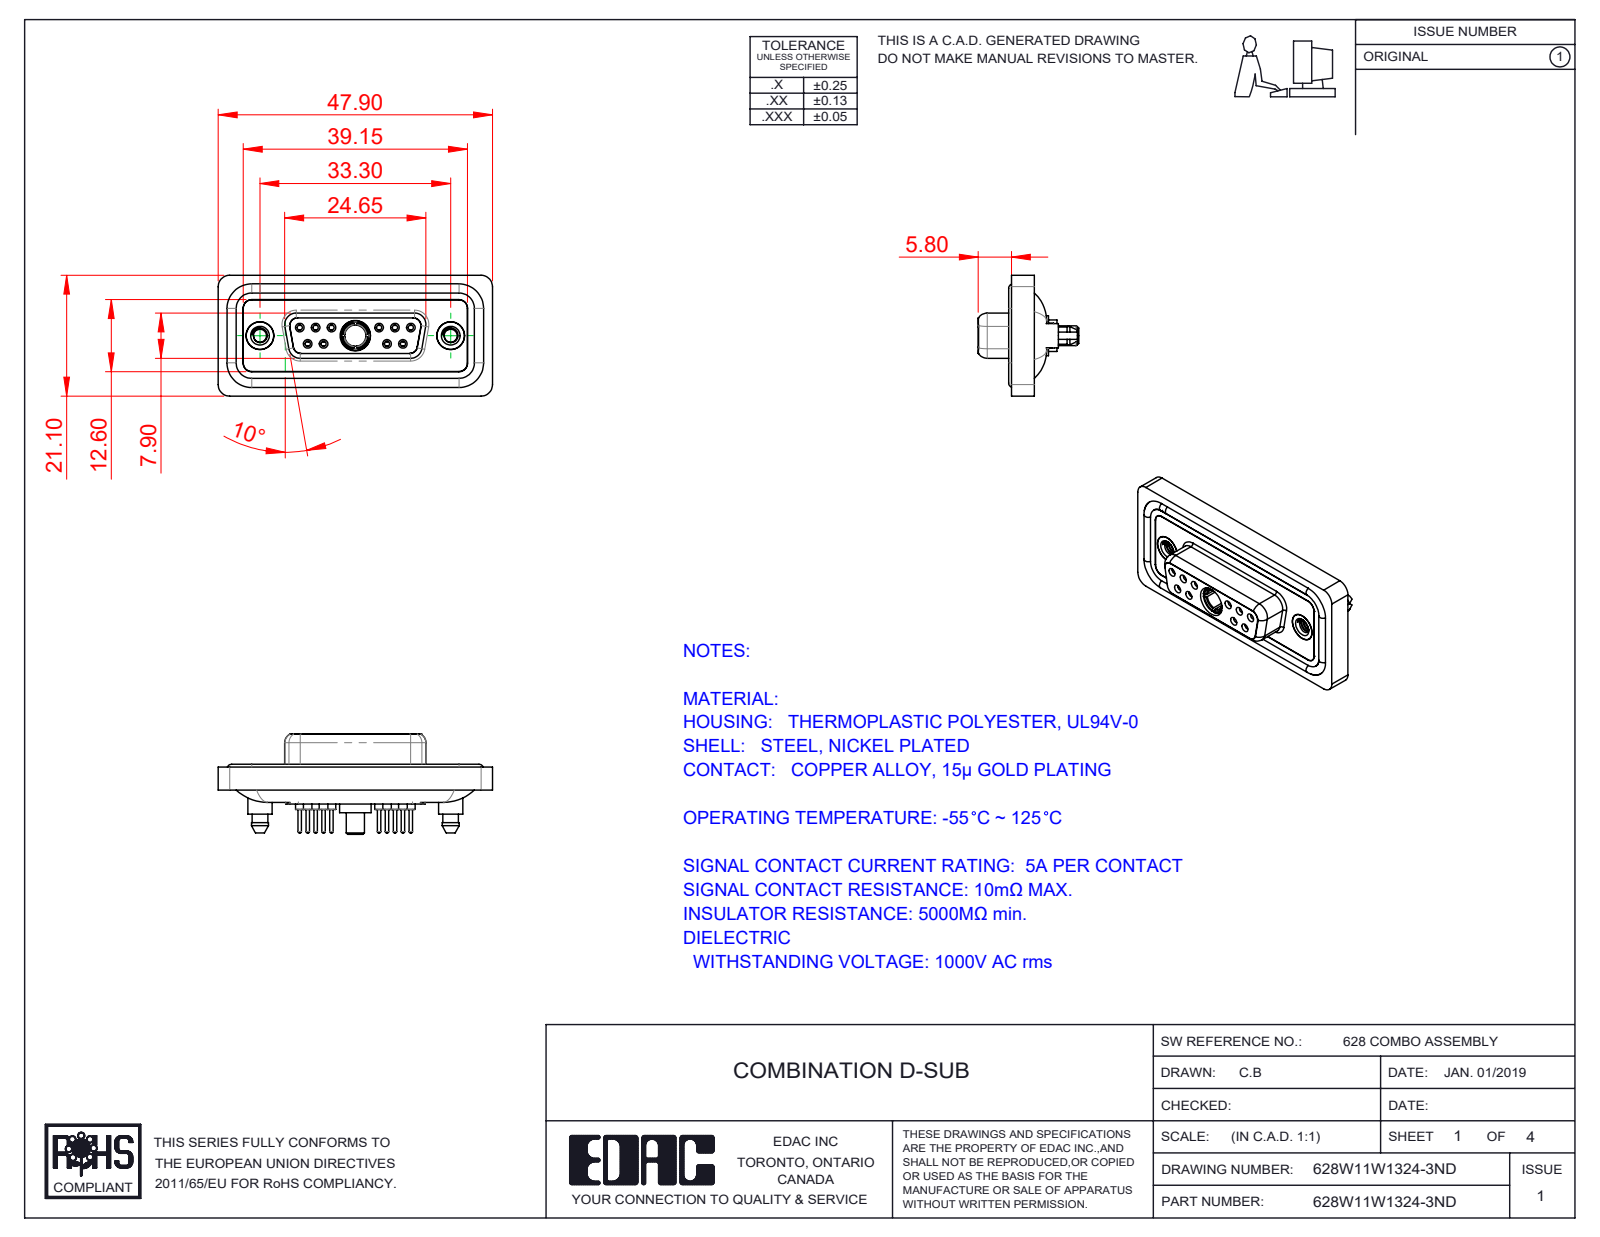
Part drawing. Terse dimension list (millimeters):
name: 628Combo Shell Front_15 Contacts; 628W11W1324-3ND; 628Combo Contact Row 1_24; 628Combo Threaded Boardlock_D (+5 more)
written by: SolidWorks 2023 (CONFIG_CONTROL_DESIGN)
unit: mm
bodies: 19 solids, 1076 faces (300 planar, 449 cylindrical, 327 other)
size: 47.9 × 21.1 × 17.55
volume: 6 269 mm³; area: 10 376 mm²
holes: 10× ⌀0.9, 10× ⌀1.1, 10× ⌀1.5, 10× ⌀2, 6× ⌀1.7, 4× ⌀1.6, 3× ⌀4.85, 2× ⌀2.26, 2× ⌀4, 2× ⌀4.05, 2× ⌀5, 1× ⌀3.7
bosses: 10× ⌀2.2, 10× ⌀1.6, 10× ⌀0.6, 2× ⌀5.4, 2× ⌀4.95, 2× ⌀4.8, 2× ⌀4.25, 1× ⌀5.5
rounds: 24× R1.5, 20× R2, 12× R1.35, 10× R1.6, 4× R0.25, 4× R0.5, 4× R0.6, 4× R0.65
face distances: 0.4, 1.6, 1.8, 2.9, 0.5, 1.1, 5.65, 7.45, 6.6, 7.05
hole spacings: 3.16, 2.77, 13.85, 11.08, 16.62, 5.03, 5.04, 5.54
